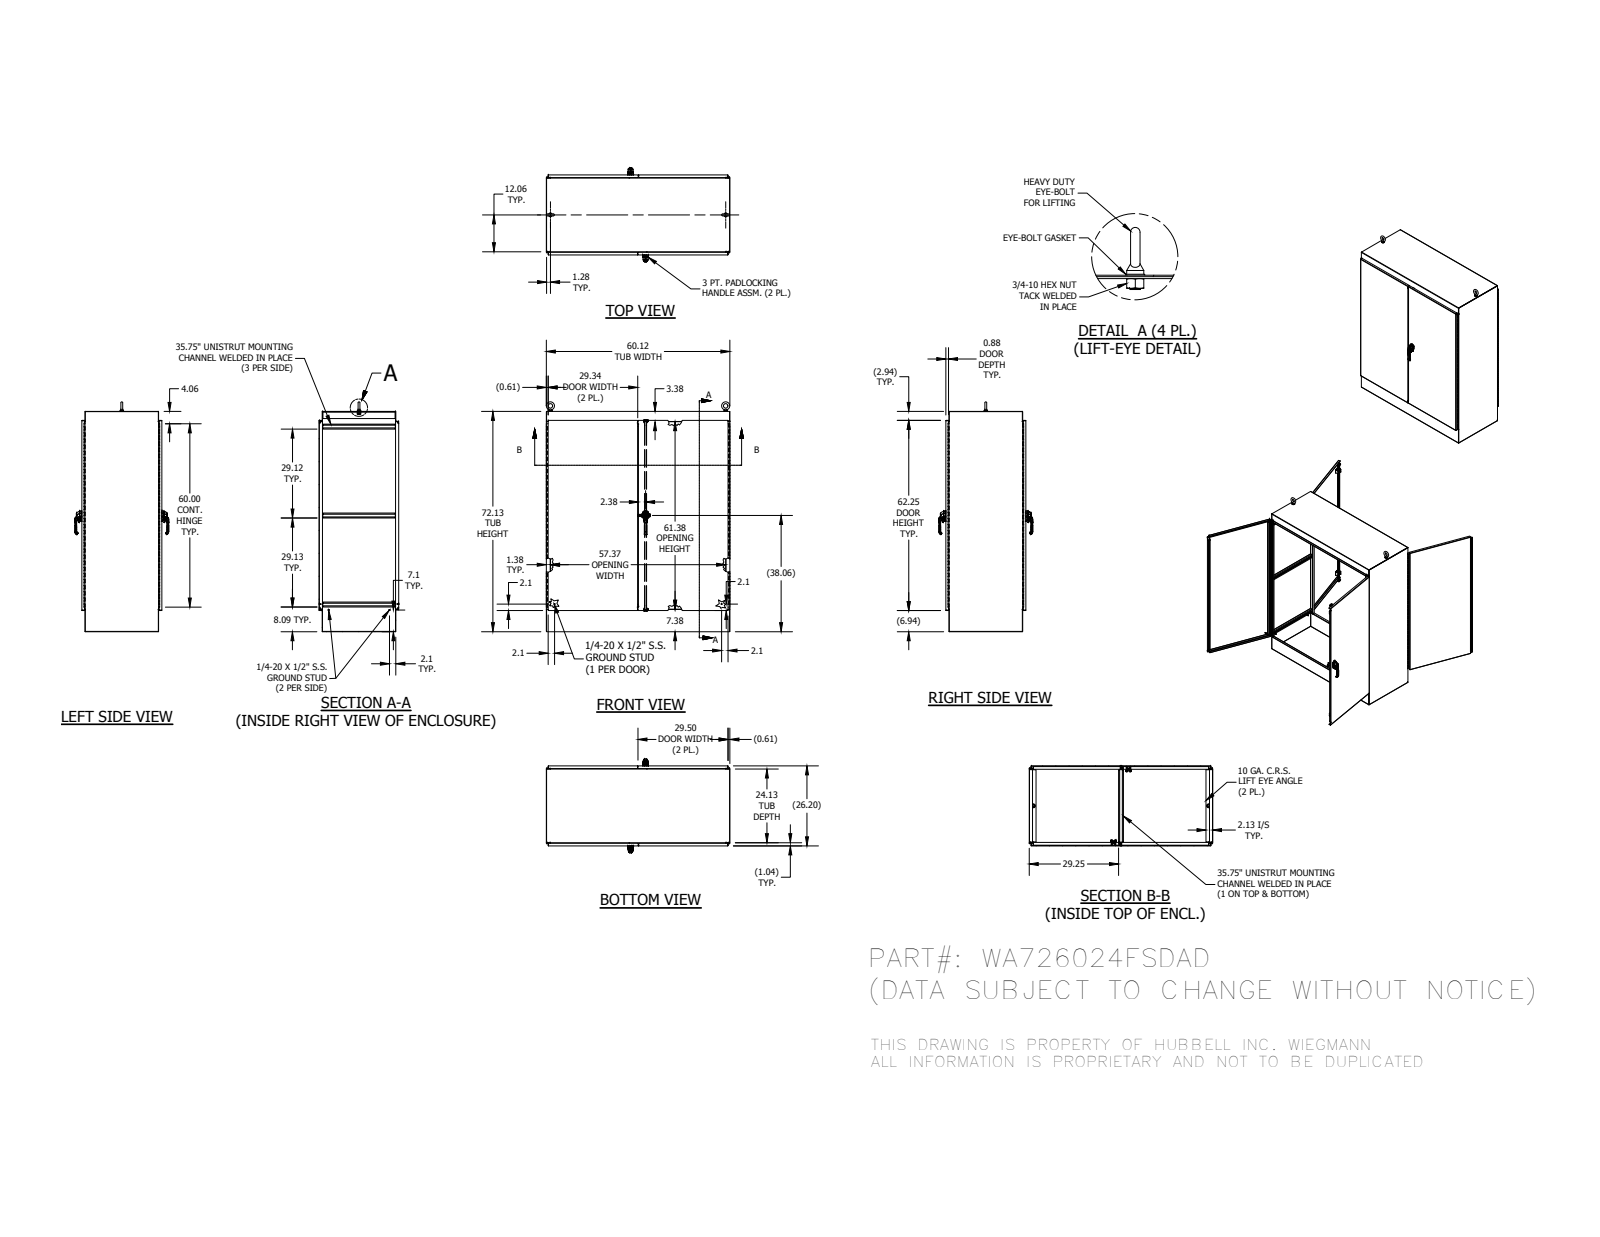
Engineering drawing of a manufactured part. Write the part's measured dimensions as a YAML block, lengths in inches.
part_name: "FUN00103; HFW3025; 316298; 349132 (+8 more)"
step_written_by: "Autodesk Inventor 2014 (AUTOMOTIVE_DESIGN)"
units: inches
bodies: {solids: 110, faces: 7244, planar: 3406, cylindrical: 2450, other: 1388}
overall_size: [75.248, 60.125, 30.733]
volume: 1838
surface_area: 38180
round_holes:
  - {diameter: 0.276, count: 16}
  - {diameter: 0.2, count: 8}
  - {diameter: 0.213, count: 6}
  - {diameter: 0.236, count: 6}
  - {diameter: 0.28, count: 6}
  - {diameter: 0.125, count: 4}
  - {diameter: 0.241, count: 4}
  - {diameter: 0.25, count: 4}
  - {diameter: 0.252, count: 4}
  - {diameter: 0.4, count: 4}
  - {diameter: 0.407, count: 4}
  - {diameter: 0.413, count: 4}
round_bosses_or_shafts:
  - {diameter: 0.25, count: 8}
  - {diameter: 1, count: 4}
  - {diameter: 0.563, count: 4}
  - {diameter: 0.526, count: 4}
  - {diameter: 0.5, count: 4}
  - {diameter: 0.375, count: 4}
  - {diameter: 0.337, count: 4}
  - {diameter: 0.313, count: 4}
partial_cylinders:
  - {radius: 0.02, count: 345}
  - {radius: 0.012, count: 170}
  - {radius: 0.031, count: 46}
  - {radius: 0.019, count: 38}
  - {radius: 0.01, count: 32}
  - {radius: 0.079, count: 30}
  - {radius: 0.125, count: 30}
  - {radius: 0.118, count: 29}
face_to_face_distances: [0.094, 26.102, 26.008, 26.196, 60.031, 1.035, 25.067, 72.031, 59.938, 60.125]
hole_center_spacings: [0.256, 0.492, 0.886, 2.028, 4.909, 4.989, 38.659, 0.38]
